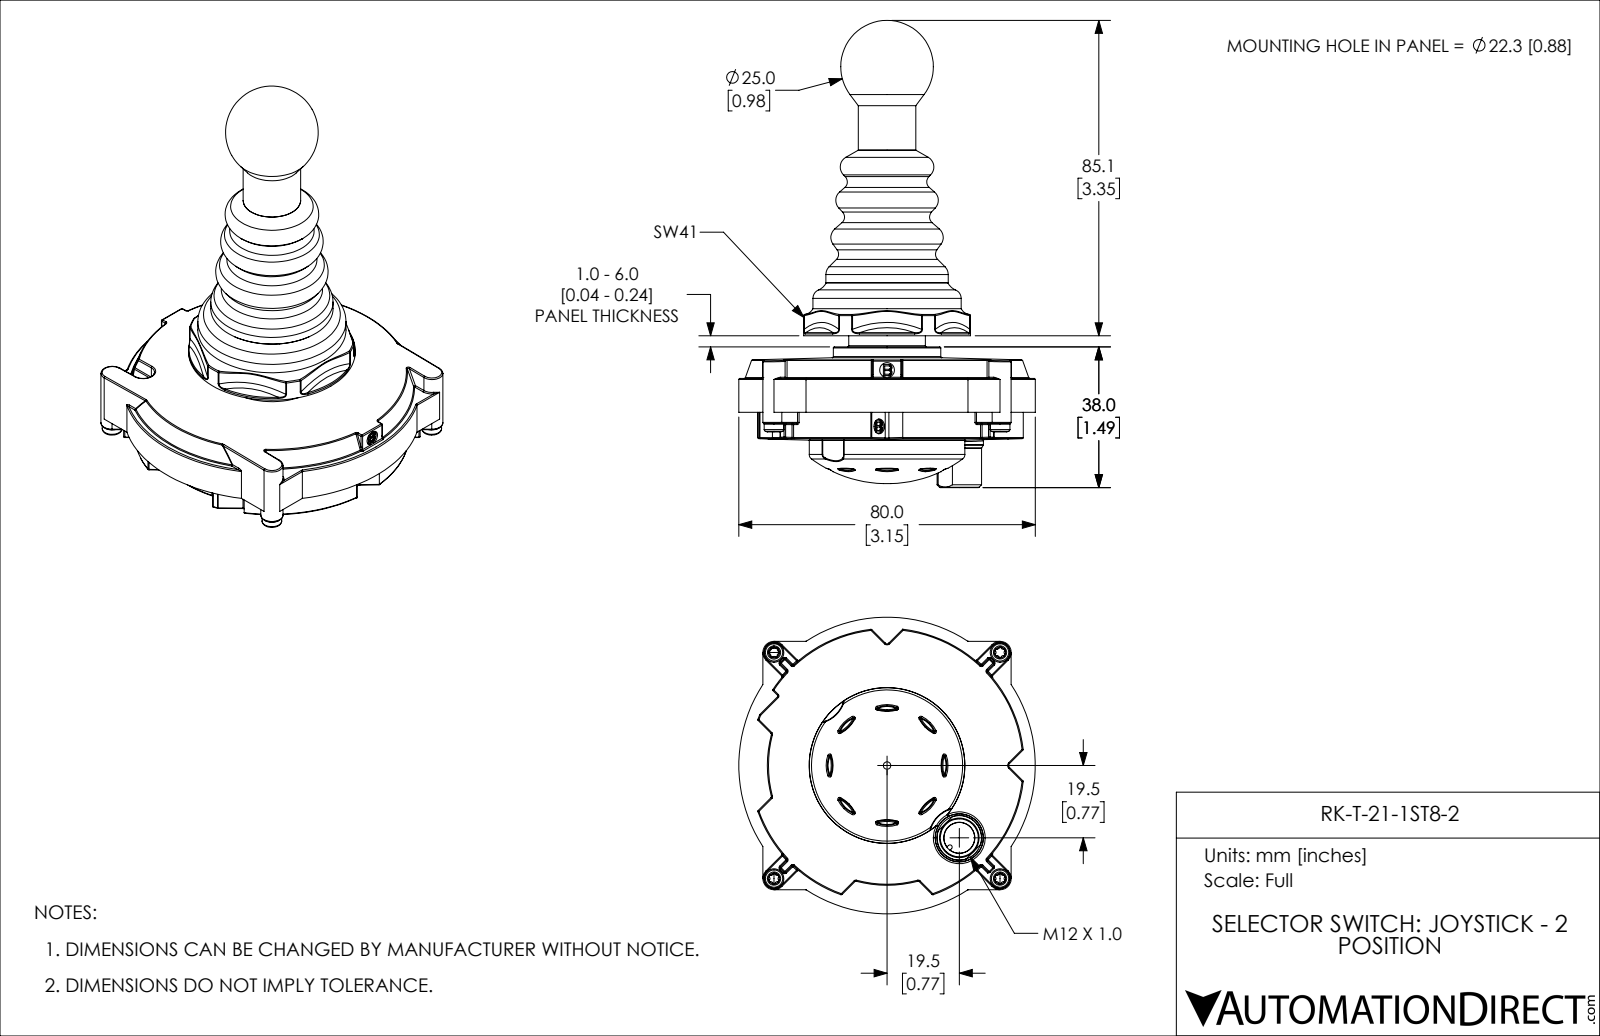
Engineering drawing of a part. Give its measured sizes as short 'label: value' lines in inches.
name: RK-T-21-1ST8-2
written by: SolidWorks 2019 (CONFIG_CONTROL_DESIGN)
unit: in
bodies: 4 solids, 1358 faces (374 planar, 341 cylindrical, 643 other)
size: 4.961 × 3.15 × 3.15
volume: 10.1 in³; area: 50.22 in²
holes: 5× ⌀0.157, 4× ⌀0.115, 1× ⌀0.327, 1× ⌀0.331, 1× ⌀1.228, 1× ⌀1.461, 1× ⌀1.579
bosses: 4× ⌀0.209, 1× ⌀1.772, 1× ⌀1.654, 1× ⌀1.575, 1× ⌀1.303, 1× ⌀1.299, 1× ⌀1.142, 1× ⌀0.984
rounds: 115× R0.012, 44× R0.007, 12× R0.02, 8× R0.102, 8× R0.354, 7× R0.024, 5× R0.118, 2× R0.027
face distances: 1.376, 0.555, 0.821, 2.638, 2.784, 1.963, 1.408, 1.016, 0.36, 0.461
hole spacings: 2.402, 1.698, 0.177, 2.016, 2.224, 3.396, 0.613, 1.086
